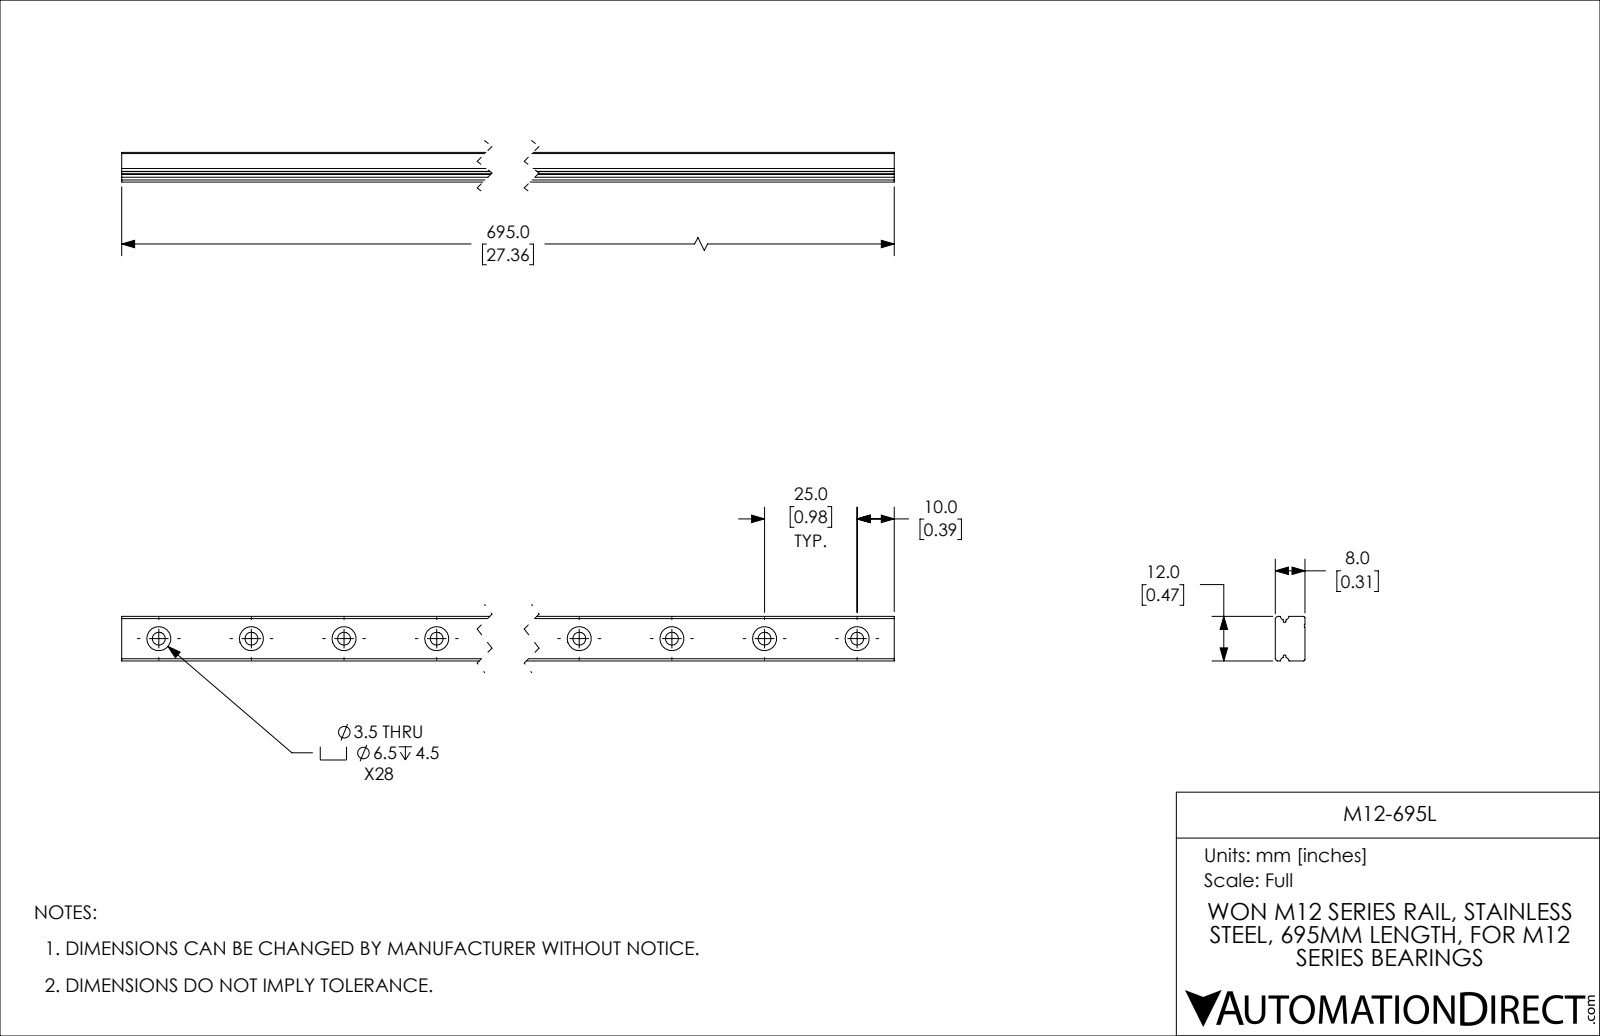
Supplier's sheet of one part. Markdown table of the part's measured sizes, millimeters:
| quantity | value |
| --- | --- |
| part name | M12-695L |
| STEP written by | SolidWorks 2019 (CONFIG_CONTROL_DESIGN) |
| units | millimeters |
| bodies | 1 solid, 165 faces (41 planar, 124 cylindrical, 0 other) |
| overall size | 695 × 12 × 8 |
| volume | 58 253 mm³ |
| surface area | 33 280 mm² |
| round holes (diameter × count) | 3.5 × 28, 6.5 × 28 |
| partial cylindrical surfaces (radius × count) | 0.42 × 2, 1 × 2, 1.15 × 2, 1.2 × 2, 0.5 × 1 |
| main face-to-face distances | 8, 12, 0.58, 3.5, 4.5, 695 |
| hole center spacings | 25, 50, 75, 100, 125, 150, 175, 200 |
